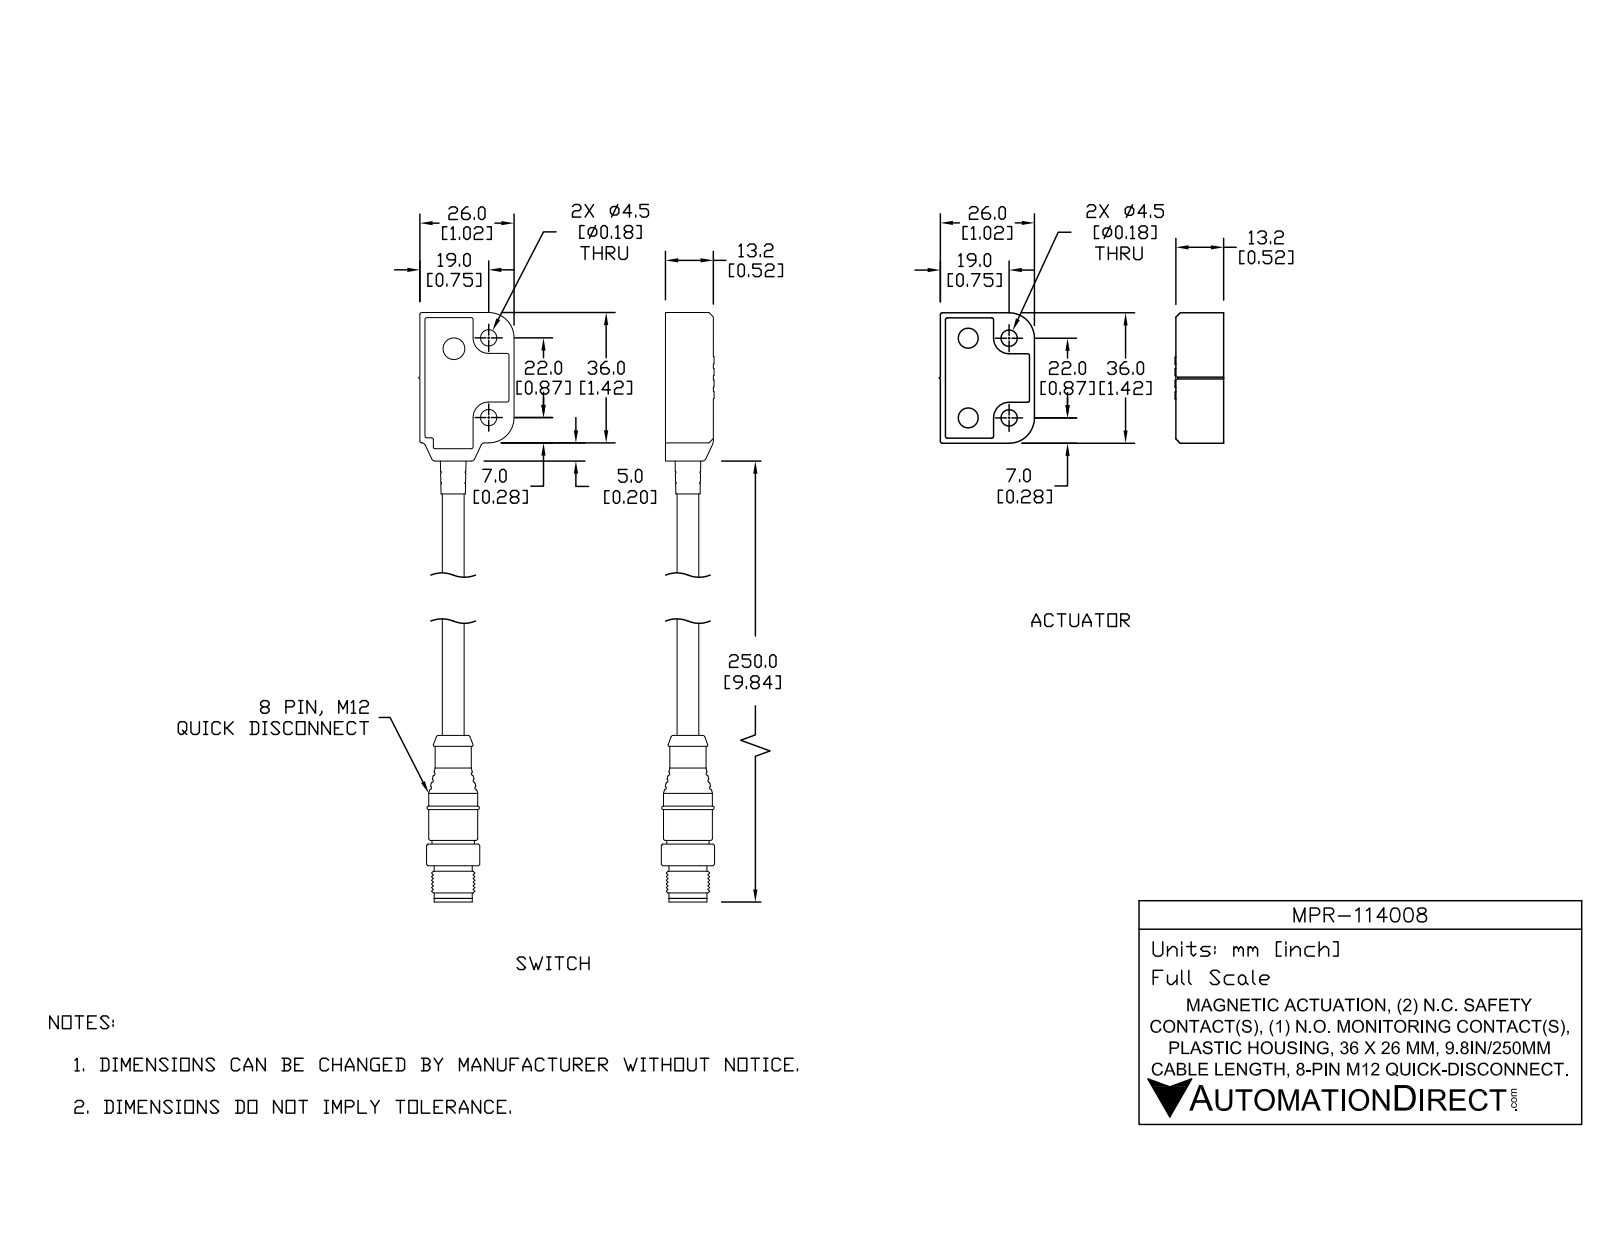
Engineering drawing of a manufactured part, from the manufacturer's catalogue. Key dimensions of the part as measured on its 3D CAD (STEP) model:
Part name (STEP PRODUCT): MPR-114008_1; MPR-114008; MPR-114008_2
STEP written by: SolidWorks 2017 (AUTOMOTIVE_DESIGN)
Units: inches
Bodies: 10 solids, 1468 faces (643 planar, 437 cylindrical, 388 other)
Overall size (bounding box): 11.457 × 2.087 × 0.579
Volume: 1.44 in³ · Surface area: 36.96 in²
Round holes (diameter × count): ⌀0.177 ×4, ⌀0.331 ×4, ⌀0.195 ×2, ⌀0.197 ×1, ⌀0.232 ×1, ⌀0.276 ×1, ⌀0.327 ×1, ⌀0.465 ×1
Round bosses / shafts (diameter × count): ⌀0.031 ×8, ⌀0.079 ×3, ⌀0.197 ×2, ⌀0.091 ×2, ⌀0.531 ×1, ⌀0.461 ×1, ⌀0.413 ×1, ⌀0.394 ×1
Partial cylindrical surfaces — rounded edges, fillets, slot ends (radius × count): R0.02 ×85, R0.008 ×30, R0.012 ×28, R0.004 ×17, R0.039 ×13, R0.169 ×4, R0.201 ×4, R0.276 ×4
Main face-to-face distances: 0.055, 0.461, 0.453, 0.39, 1.063, 0.047, 0.059, 0.094, 0.445, 0.5
Hole centre spacings: 0.866, 0.445, 0.974, 1.091, 1.393, 1.535, 1.763, 0.396
